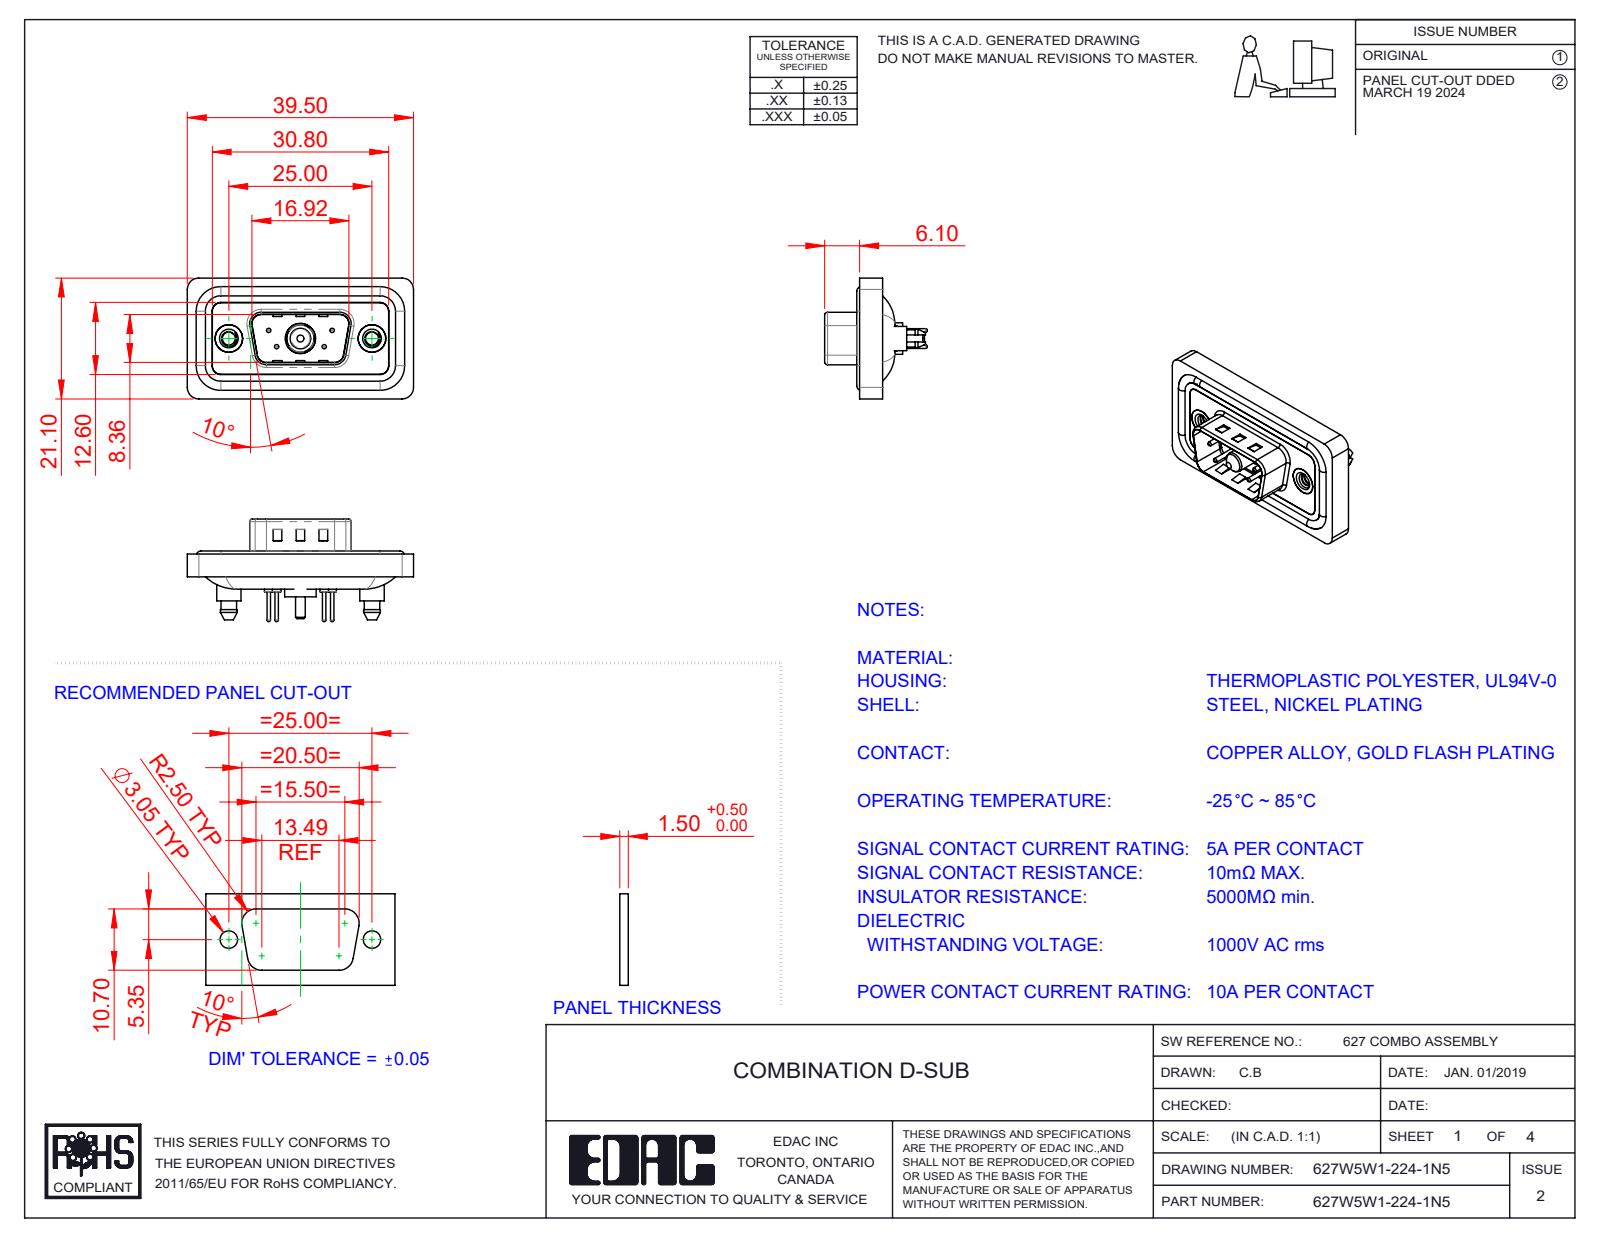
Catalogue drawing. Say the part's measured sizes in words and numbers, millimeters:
The part is named "627Combo Waterproof Housing_09 Contacts; 627Combo Contact Row 1_24; 627Combo Housing_5W1; 627Combo Shell Rear_09 Contacts (+5 more)". Its 3-D file was written by "SolidWorks 2023 (CONFIG_CONTROL_DESIGN)". It is 13 solids with 648 faces: 199 planar, 287 cylindrical and 162 other. Overall it measures 39.5 by 21.1 by 17.9 millimeters. Its volume is 4 507 cubic millimeters and its surface area 7 262 square millimeters. Round holes: 4 of diameter 0.75, 4 of diameter 1.6, 4 of diameter 2, 2 of diameter 2.26, 2 of diameter 4, 2 of diameter 4.8, 2 of diameter 5, 1 of diameter 4.85, 1 of diameter 5.3. Round bosses or shafts: 4 of diameter 1.6, 4 of diameter 1.5, 4 of diameter 0.6, 2 of diameter 5.4, 2 of diameter 4.9, 2 of diameter 4.25, 1 of diameter 5.5, 1 of diameter 5.2. Partial cylindrical surfaces (rounded edges, fillets, slot ends): 24 of radius 1.5, 18 of radius 2, 10 of radius 1.6, 8 of radius 0.5, 4 of radius 0.25, 4 of radius 0.6, 4 of radius 0.65, 4 of radius 0.9. The main face-to-face distances are 0.4, 1.1, 2.9, 1.6, 1.5, 3.1, 0.5, 2.5, 4, 0.7. The hole center spacings are 3.16, 5.72, 7.1, 12.5, 18.1, 4.39, 4.4, 8.31.
